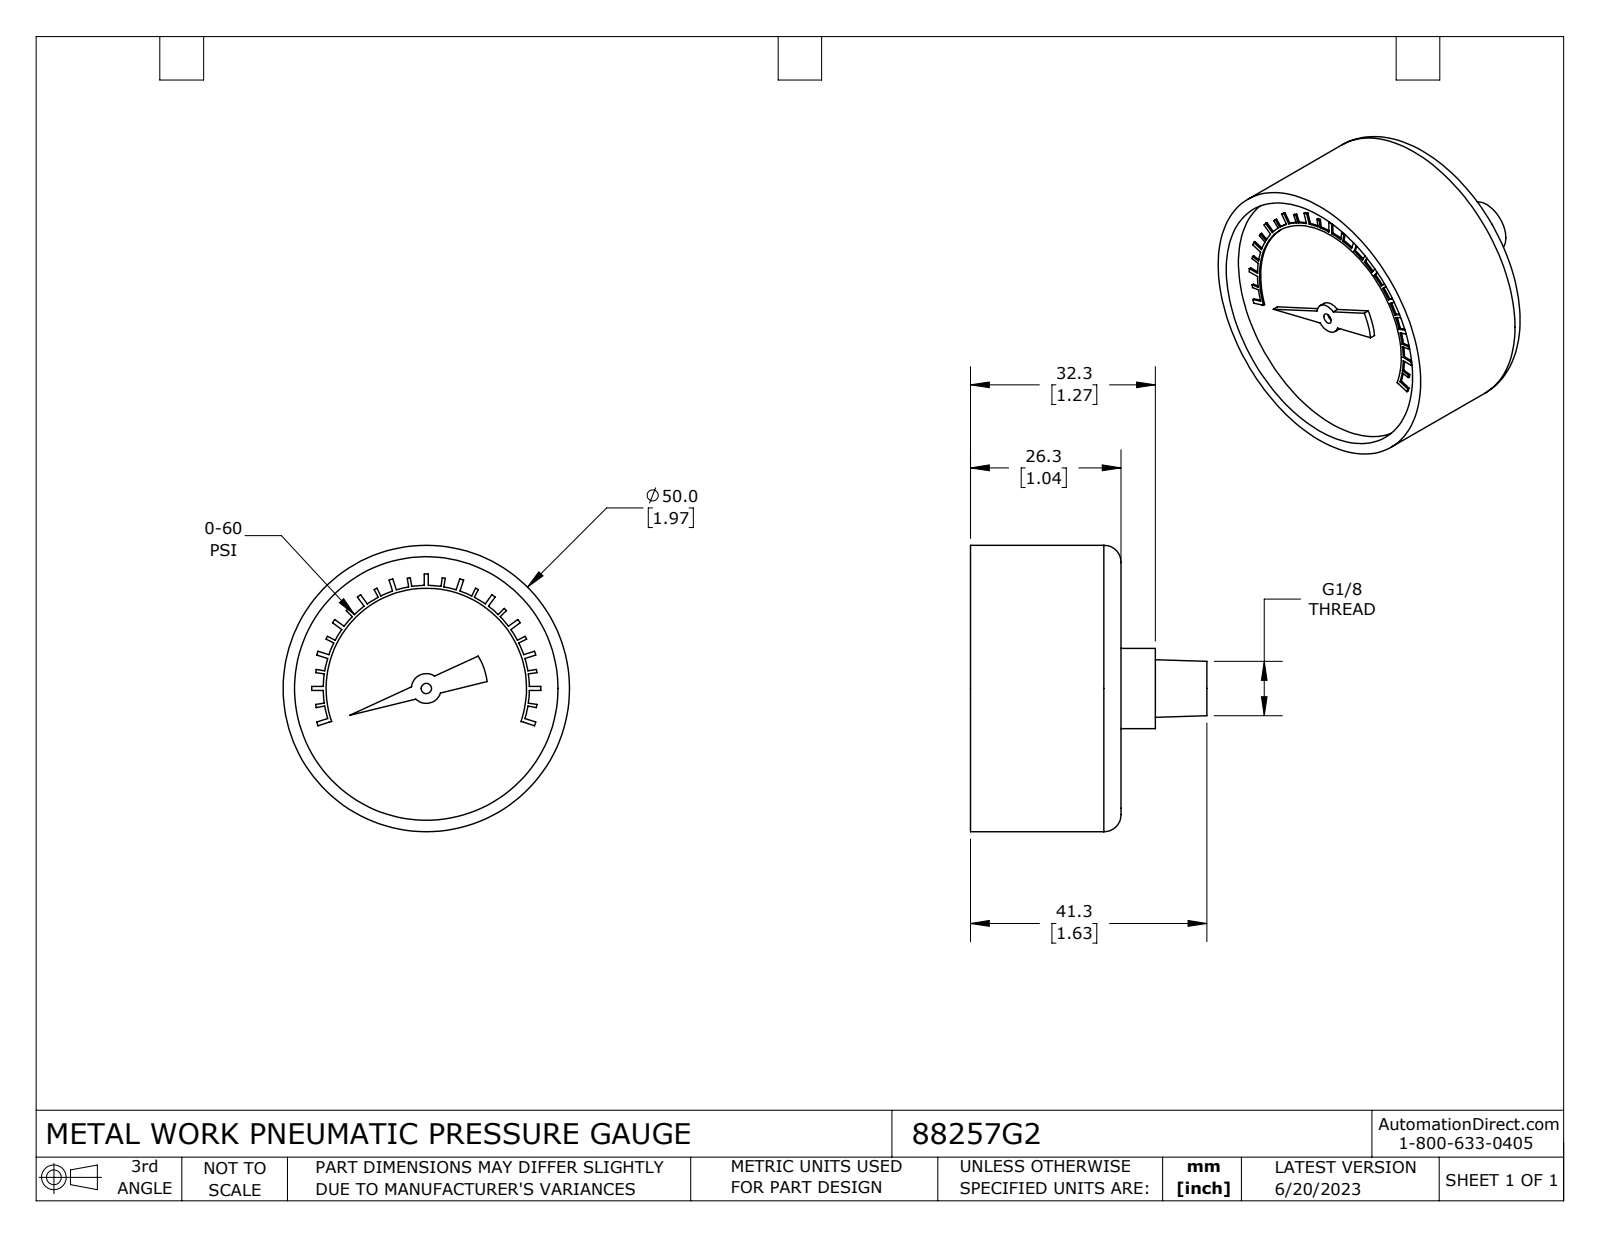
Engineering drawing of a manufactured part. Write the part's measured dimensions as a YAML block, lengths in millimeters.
part_name: "88257G2"
step_written_by: "SolidWorks 2021 (CONFIG_CONTROL_DESIGN)"
units: millimeters
bodies: {solids: 1, faces: 133, planar: 93, cylindrical: 36, other: 4}
overall_size: [50, 50, 41.3]
volume: 48340
surface_area: 9026
round_holes:
  - {diameter: 1.8, count: 1}
  - {diameter: 46, count: 1}
round_bosses_or_shafts:
  - {diameter: 50, count: 1}
partial_cylinders:
  - {radius: 2.6, count: 1}
  - {radius: 10.7, count: 1}
  - {radius: 17.4, count: 1}
  - {radius: 17.4, count: 1}
  - {radius: 17.5, count: 1}
  - {radius: 17.5, count: 1}
  - {radius: 17.6, count: 1}
  - {radius: 18, count: 1}
face_to_face_distances: [23.3, 26.3, 3, 14, 6, 29.3, 32.3, 9, 15, 38.3]
